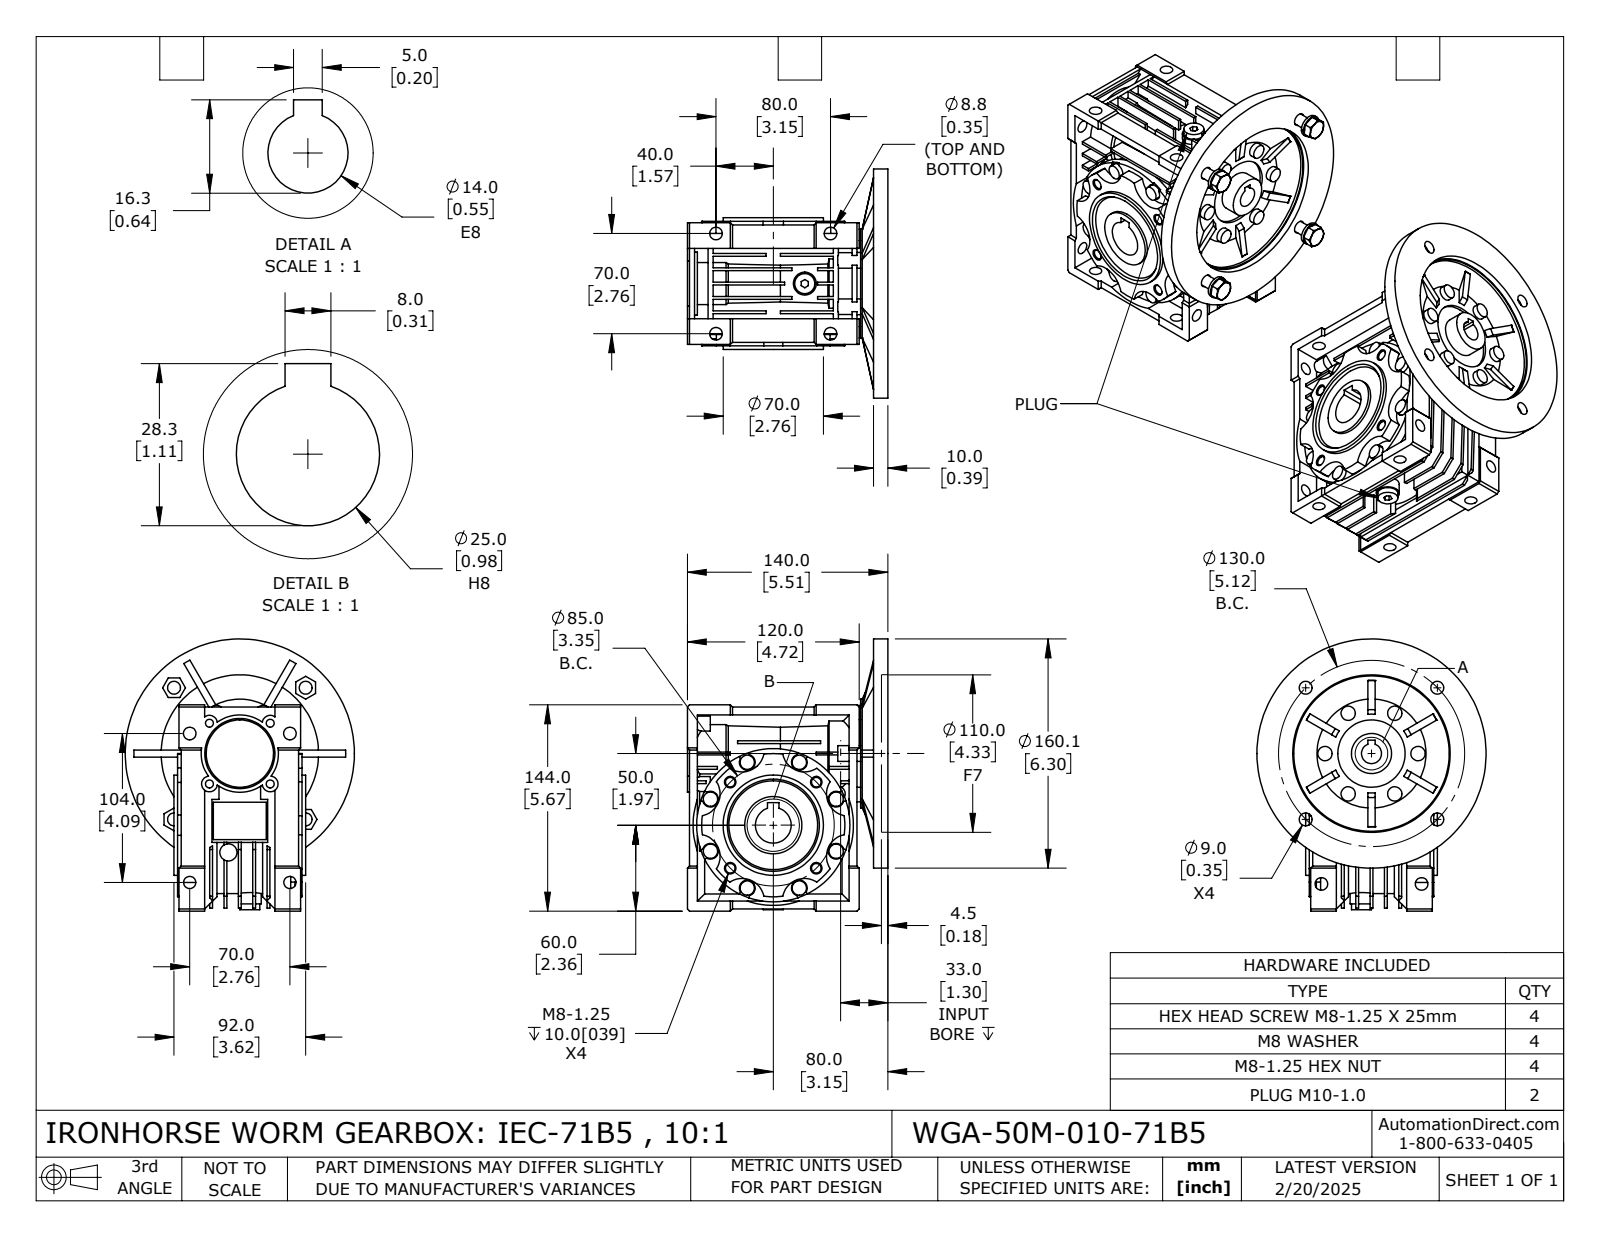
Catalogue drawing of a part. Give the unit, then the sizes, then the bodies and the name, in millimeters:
Units: millimetres
Overall size (bounding box): 190.03 × 160.06 × 140
Round holes (diameter × count): ⌀8.8 ×8, ⌀8.5 ×6, ⌀9 ×6, ⌀5.55 ×4, ⌀6.65 ×2, ⌀6.65 ×2, ⌀14 ×1, ⌀15 ×1, ⌀25 ×1, ⌀28 ×1, ⌀34 ×1, ⌀40 ×1
Round bosses / shafts (diameter × count): ⌀10 ×14, ⌀16 ×2, ⌀14 ×2, ⌀9.8 ×2, ⌀8.3 ×2, ⌀160.06 ×1, ⌀107 ×1, ⌀76 ×1
Partial cylindrical surfaces — rounded edges, fillets, slot ends (radius × count): R5.5 ×18, R6 ×8, R15 ×8, R15.5 ×8, R20.76 ×1, R46 ×1, R47.7 ×1, R50 ×1
Main face-to-face distances: 10, 2, 7, 5.5, 8, 1.5, 20, 5, 55, 35
Hole centre spacings: 71.58, 70, 30, 35, 42.42, 42.5, 60.1, 65
Volume: 1 146 000 mm³ · Surface area: 256 628 mm²
Bodies: 7 solids, 1007 faces (577 planar, 316 cylindrical, 114 other)
Part name (STEP PRODUCT): WGA-50M-010-71B5
STEP written by: SolidWorks 2024 (CONFIG_CONTROL_DESIGN)
